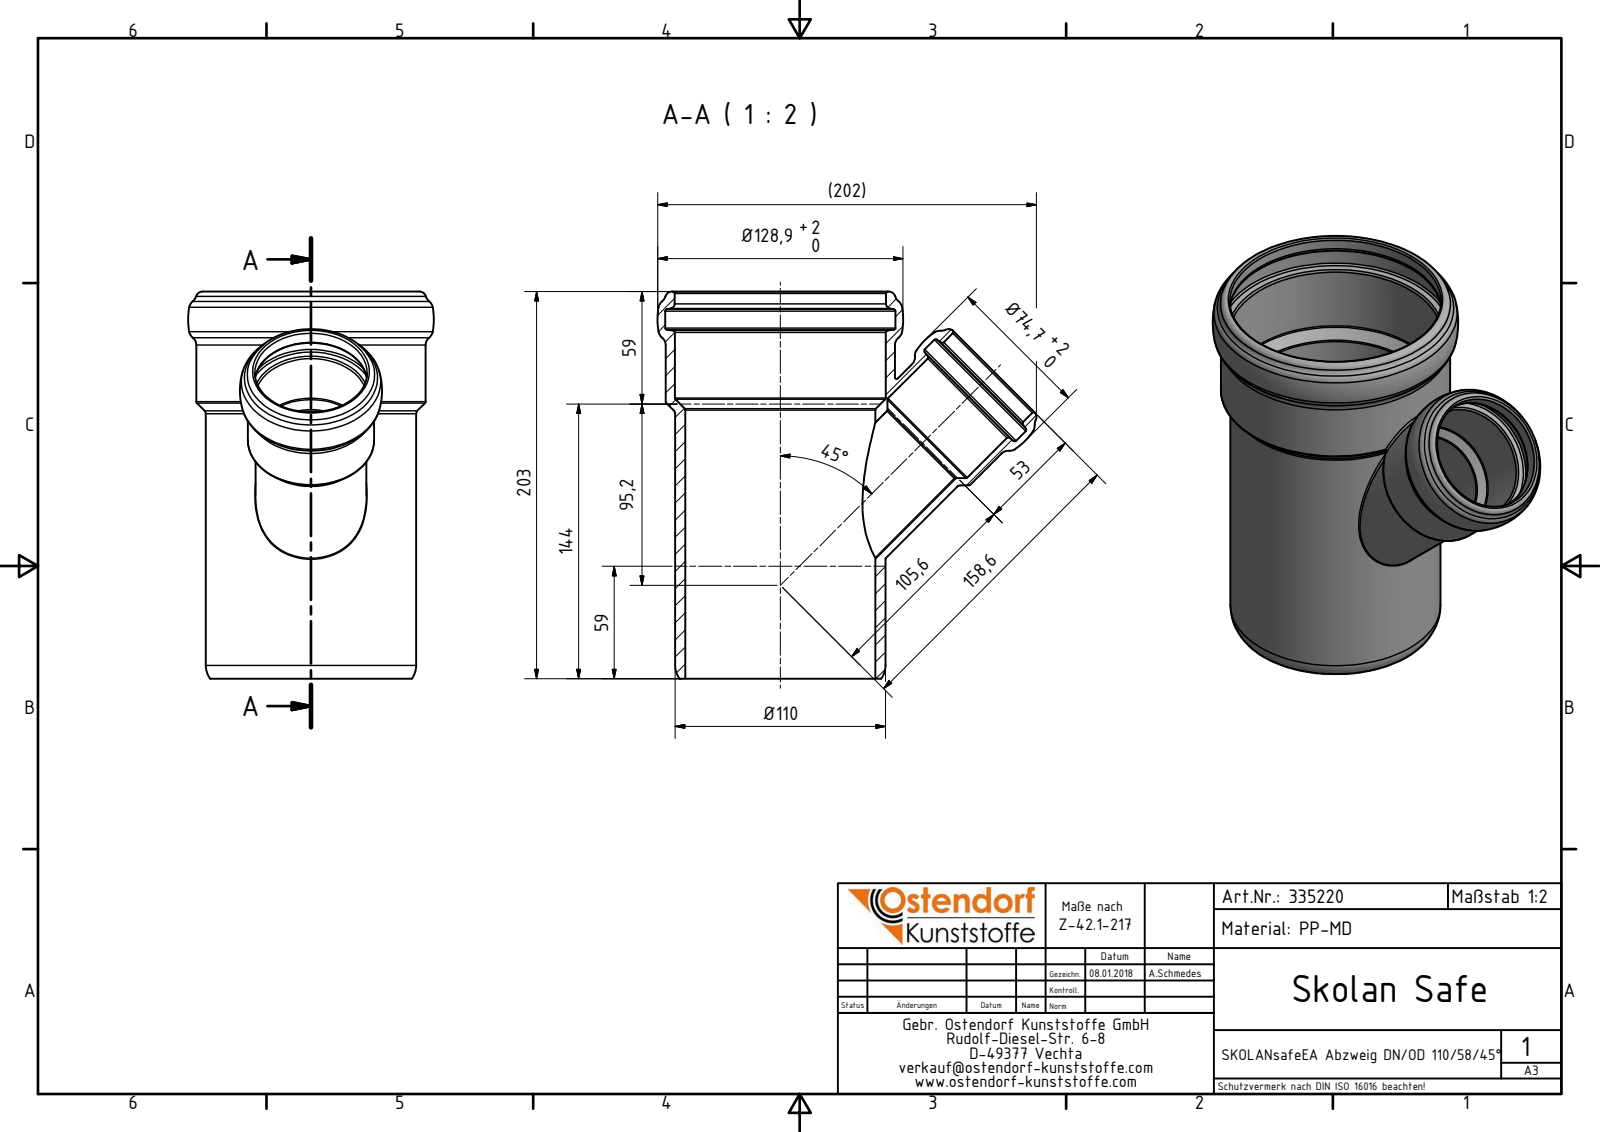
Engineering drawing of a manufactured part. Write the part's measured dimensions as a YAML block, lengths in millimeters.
part_name: "335220 SKOLANsafeEA Abzweiger DN_OD 110_58_45°"
step_written_by: "Autodesk Inventor 2016 (AUTOMOTIVE_DESIGN)"
units: millimeters
bodies: {solids: 1, faces: 68, planar: 1, cylindrical: 12, other: 55}
overall_size: [203.2, 198.95, 128.9]
volume: 416814
surface_area: 175059
round_holes:
  - {diameter: 50.2, count: 1}
  - {diameter: 58.8, count: 1}
  - {diameter: 59, count: 1}
  - {diameter: 67.9, count: 1}
  - {diameter: 99.8, count: 1}
  - {diameter: 110.8, count: 1}
  - {diameter: 111, count: 1}
  - {diameter: 120.9, count: 1}
round_bosses_or_shafts:
  - {diameter: 120.4, count: 1}
  - {diameter: 110.4, count: 1}
  - {diameter: 66.4, count: 1}
  - {diameter: 58.2, count: 1}
